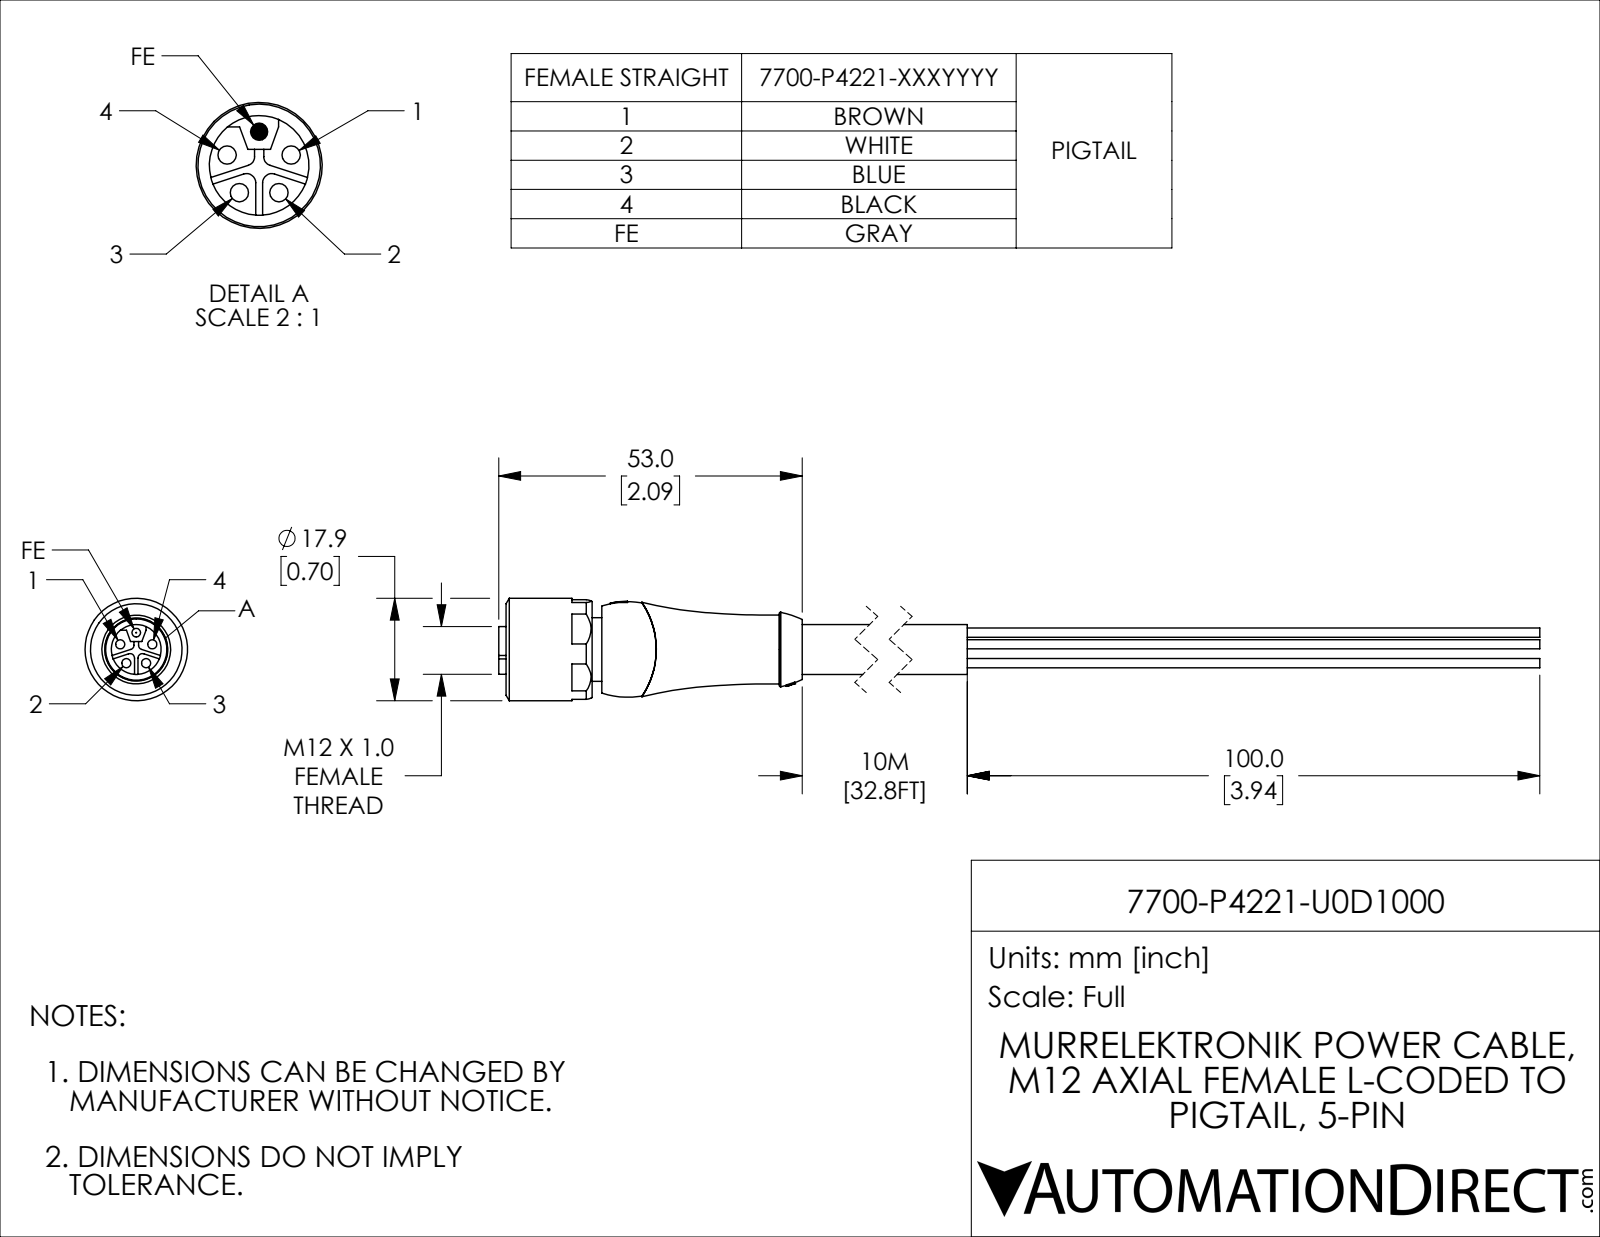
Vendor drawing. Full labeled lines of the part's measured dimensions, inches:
Part name (STEP PRODUCT): 7700-P4221-U0D1000
STEP written by: SolidWorks 2021 (CONFIG_CONTROL_DESIGN)
Units: inches
Bodies: 2 solids, 142 faces (69 planar, 40 cylindrical, 33 other)
Overall size (bounding box): 7.598 × 0.705 × 0.705
Volume: 0.735 in³ · Surface area: 12.83 in²
Round holes (diameter × count): ⌀0.063 ×4, ⌀0.433 ×1, ⌀0.512 ×1
Round bosses / shafts (diameter × count): ⌀0.705 ×1, ⌀0.51 ×1, ⌀0.437 ×1, ⌀0.343 ×1, ⌀0.063 ×1, ⌀0.059 ×1
Partial cylindrical surfaces — rounded edges, fillets, slot ends (radius × count): R0.031 ×4
Main face-to-face distances: 0.657, 0.591, 0.067, 0.667, 3.61, 3.02, 2.953, 0.181, 0.362, 0.228
Hole centre spacings: 0.116, 0.136, 0.22
